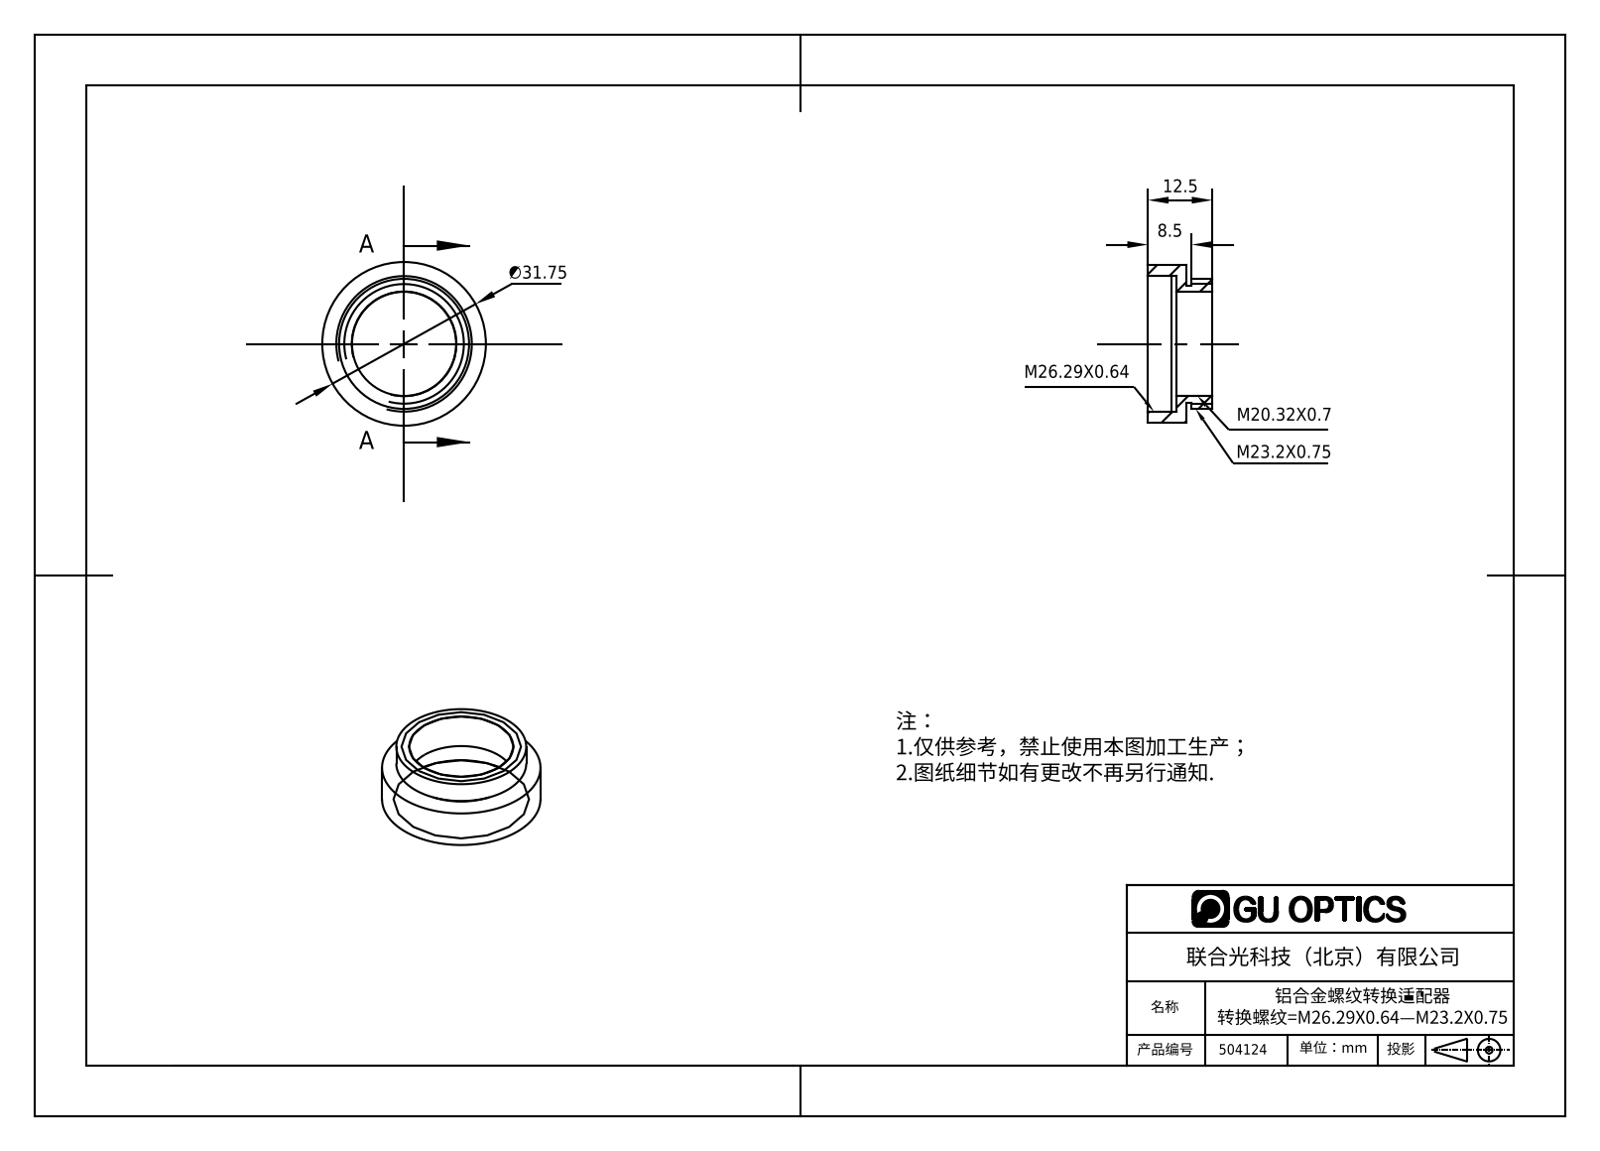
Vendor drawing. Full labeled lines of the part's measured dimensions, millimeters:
Part name (STEP PRODUCT): 504124
STEP written by: SolidWorks 2016 (AUTOMOTIVE_DESIGN)
Units: millimetres
Bodies: 1 solid, 18 faces (6 planar, 12 cylindrical, 0 other)
Overall size (bounding box): 31.75 × 31.75 × 12.5
Volume: 3 120 mm³ · Surface area: 3 191 mm²
Round holes (diameter × count): ⌀20.2 ×1, ⌀26.2 ×1, ⌀26.5 ×1
Round bosses / shafts (diameter × count): ⌀31.75 ×1, ⌀25.22 ×1, ⌀22.7 ×1
Main face-to-face distances: 7.5, 5.5, 2, 12.5, 7, 5, 1, 3, 4, 8.5
